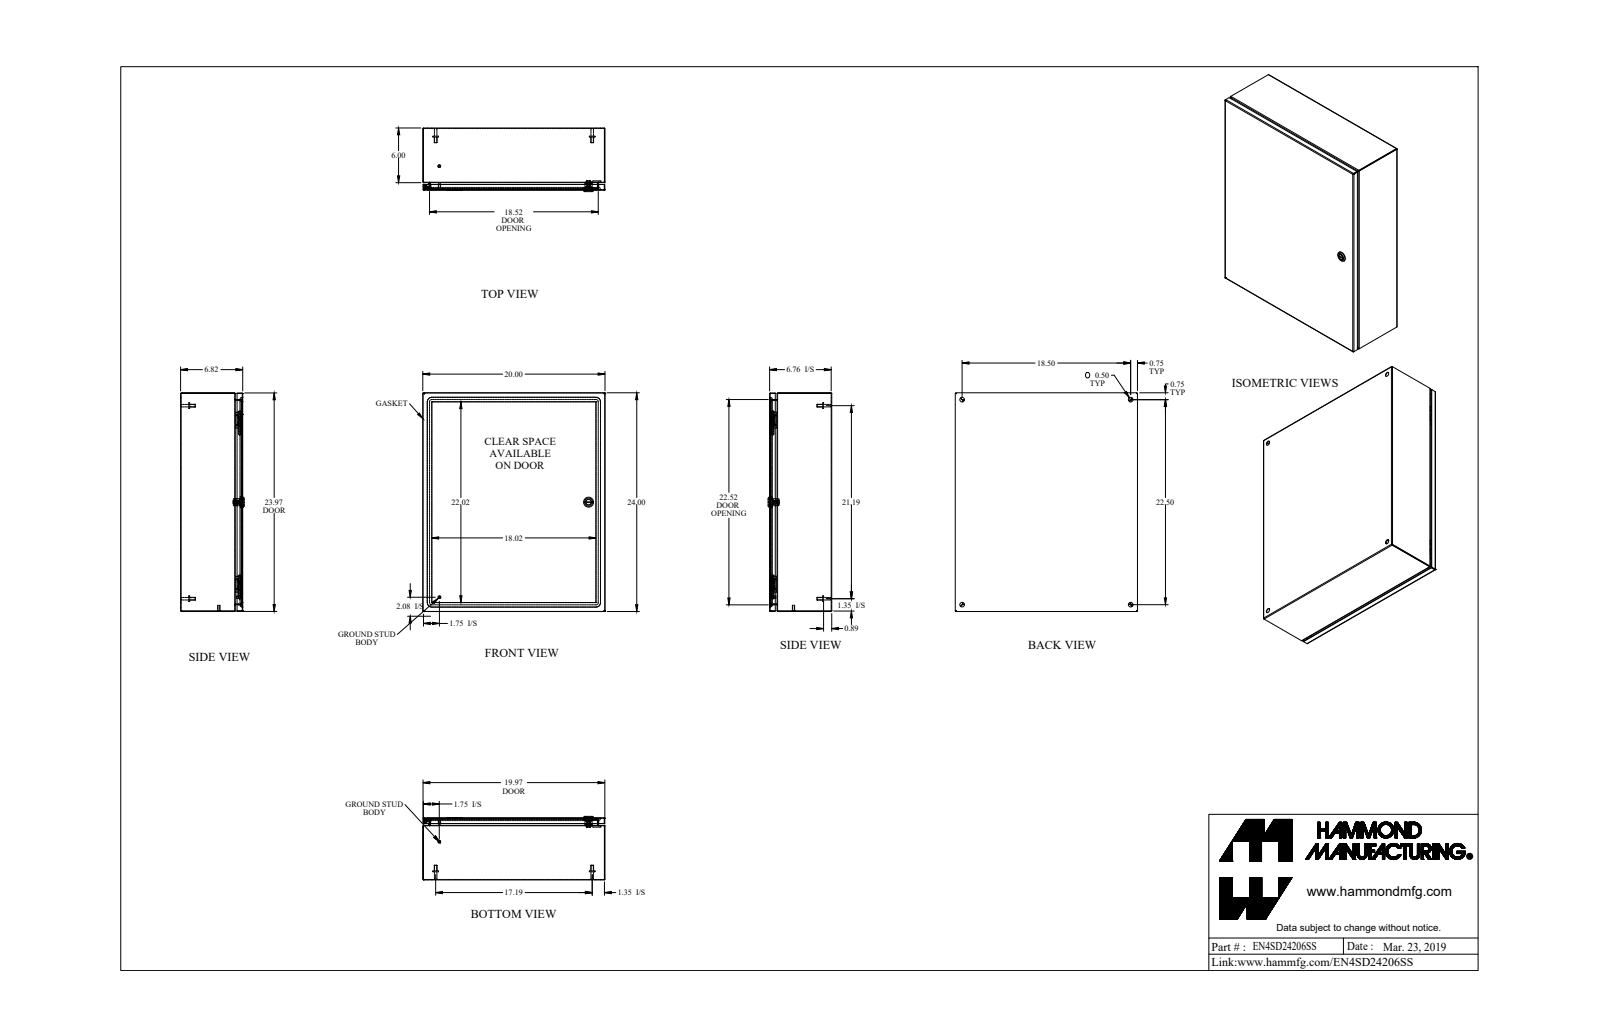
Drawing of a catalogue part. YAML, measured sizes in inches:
part_name: "EN4SD24206SS_Default"
step_written_by: "SolidWorks 2019 (CONFIG_CONTROL_DESIGN)"
units: inches
bodies: {solids: 22, faces: 657, planar: 303, cylindrical: 212, other: 142}
overall_size: [24, 20, 6.982]
volume: 103.2
surface_area: 3517
round_holes:
  - {diameter: 0.5, count: 5}
  - {diameter: 0.172, count: 1}
  - {diameter: 0.197, count: 1}
  - {diameter: 0.24, count: 1}
  - {diameter: 0.242, count: 1}
  - {diameter: 0.387, count: 1}
  - {diameter: 0.63, count: 1}
  - {diameter: 0.768, count: 1}
round_bosses_or_shafts:
  - {diameter: 0.313, count: 6}
  - {diameter: 0.625, count: 5}
  - {diameter: 0.275, count: 4}
  - {diameter: 0.25, count: 2}
  - {diameter: 1.1, count: 1}
  - {diameter: 0.785, count: 1}
  - {diameter: 0.525, count: 1}
  - {diameter: 0.455, count: 1}
partial_cylinders:
  - {radius: 0.029, count: 21}
  - {radius: 0.086, count: 21}
  - {radius: 0.188, count: 12}
  - {radius: 0.006, count: 4}
  - {radius: 0.062, count: 4}
  - {radius: 0.25, count: 4}
  - {radius: 0.499, count: 4}
  - {radius: 0.125, count: 2}
face_to_face_distances: [0.057, 6.765, 6.708, 6.822, 19.943, 23.943, 19.886, 20, 23.886, 24]
hole_center_spacings: [11.3, 18.5, 20.754, 22.5, 29.129]
